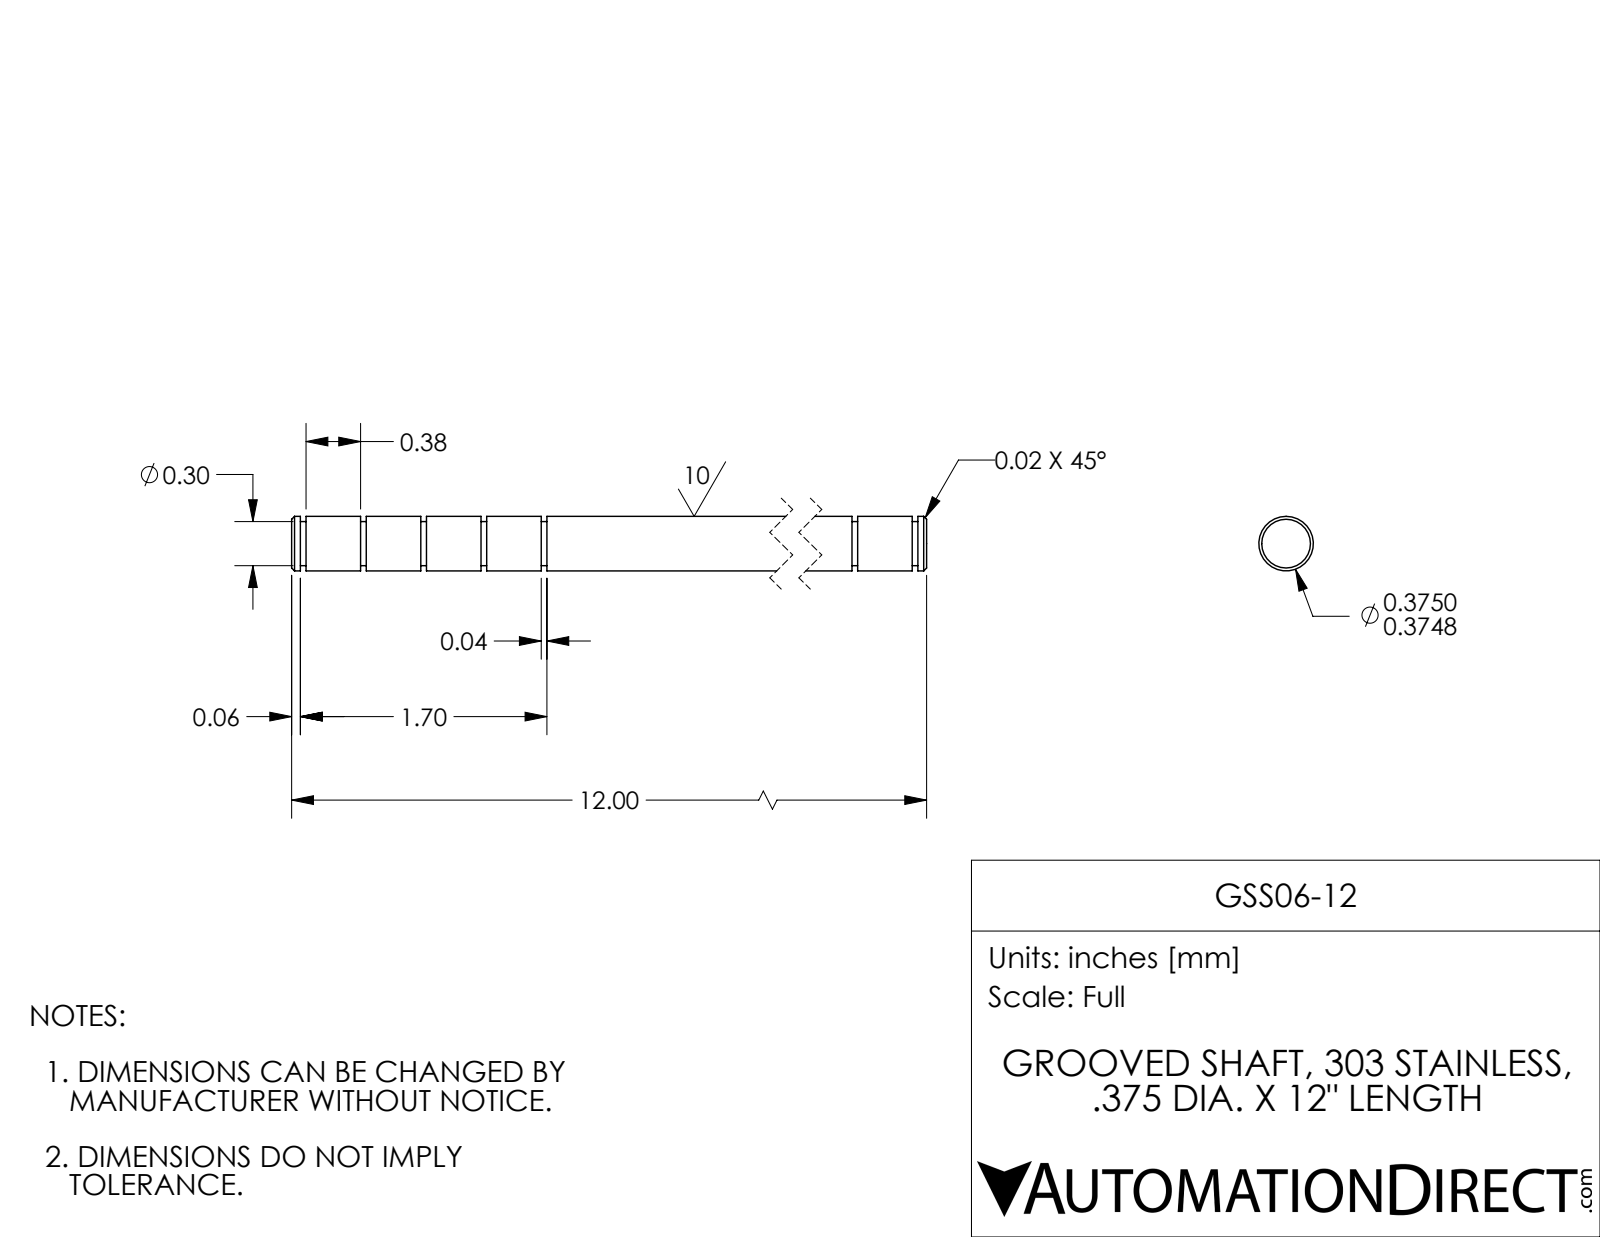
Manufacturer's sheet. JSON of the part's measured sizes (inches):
{"part_name": "GSS06-12", "step_written_by": "SolidWorks 2017 (AUTOMOTIVE_DESIGN)", "units": "inches", "bodies": {"solids": 1, "faces": 50, "planar": 16, "cylindrical": 30, "other": 4}, "overall_size": [12, 0.375, 0.375], "volume_in3": 1.314, "surface_area_in2": 14.8, "round_bosses_or_shafts": [[0.375, 1], [0.303, 1]], "face_to_face_distances": [0.414, 0.039, 11.427, 0.828, 11.013, 0.453, 0.375, 1.242, 10.185, 12]}
